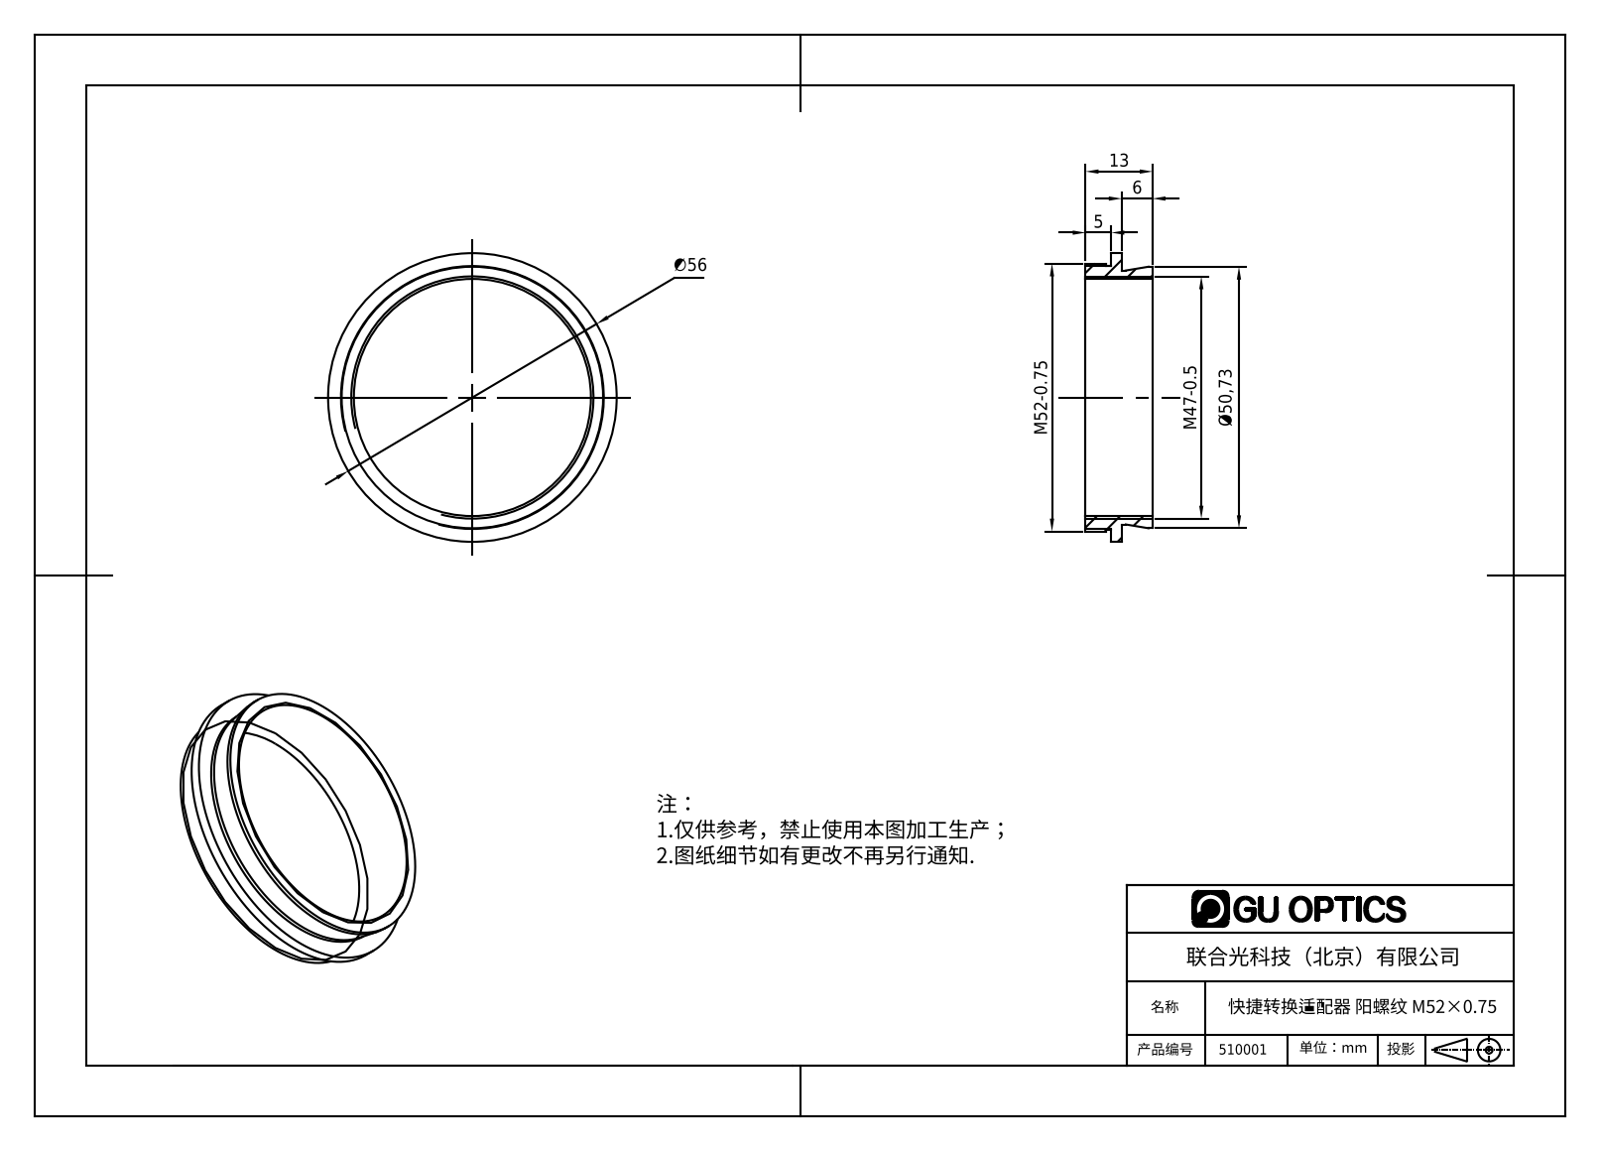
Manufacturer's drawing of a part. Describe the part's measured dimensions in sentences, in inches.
The part is named "510001". Its 3-D file was written by "SolidWorks 2016 (CONFIG_CONTROL_DESIGN)". It is 1 solid with 19 faces: 5 planar, 12 cylindrical and 2 other. Overall it measures 2.205 by 2.205 by 0.512 inches. Its volume is 0.345 cubic inches and its surface area 9.057 square inches. Round holes: 1 of diameter 1.811. Round bosses or shafts: 1 of diameter 2.205, 1 of diameter 2.047, 1 of diameter 2.016, 1 of diameter 1.997, 1 of diameter 1.94. The main face-to-face distances are 0.276, 0.197, 0.079, 0.512, 0.315, 0.236, 0.157, 0.039, 0.118, 0.354.
